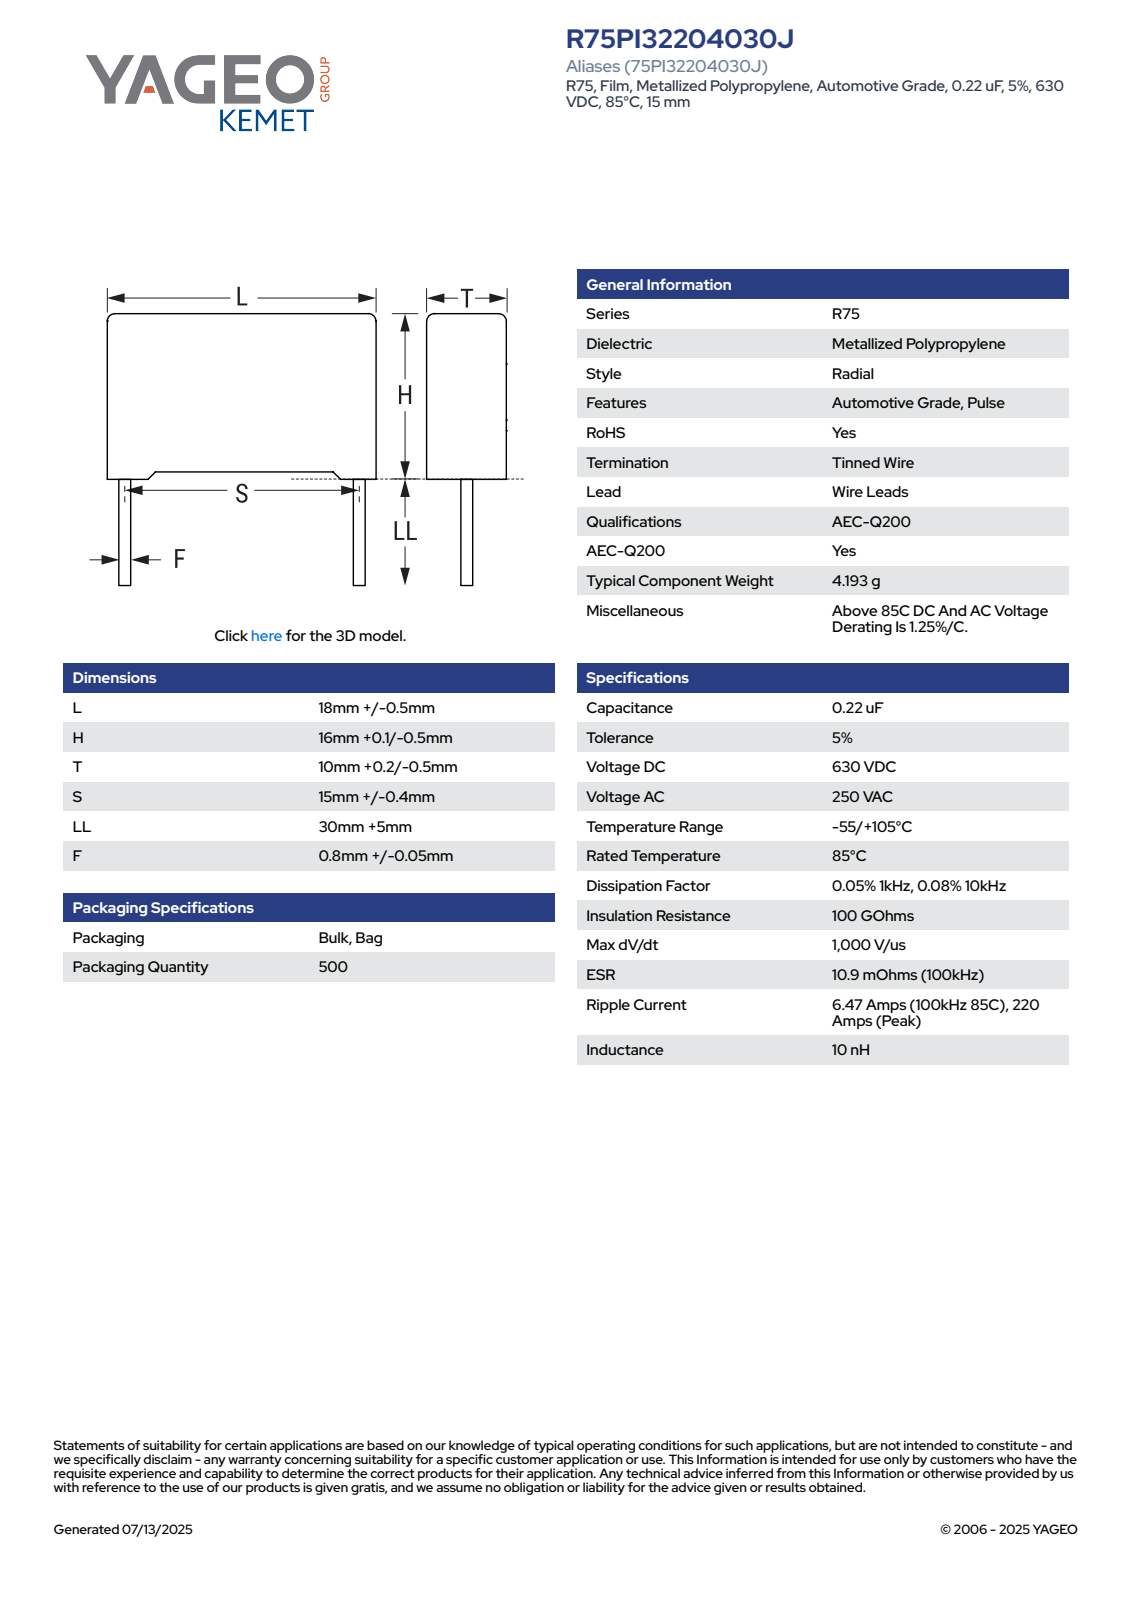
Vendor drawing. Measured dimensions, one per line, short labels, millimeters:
name: CFR_RB2_18X16X10_L18.5H16.1T10.2S15LL35F0.85
written by: SolidWorks 2021 (AUTOMOTIVE_DESIGN)
unit: mm
bodies: 4 solids, 85 faces (77 planar, 8 cylindrical, 0 other)
size: 51.1 × 18.5 × 10.21
volume: 2 952 mm³; area: 1 520 mm²
bosses: 2× ⌀0.85
rounds: 4× R0.5
face distances: 10.2, 18.5, 15.35, 0.62, 0.75, 16.1, 0.56, 15.54, 17.88, 9.58
